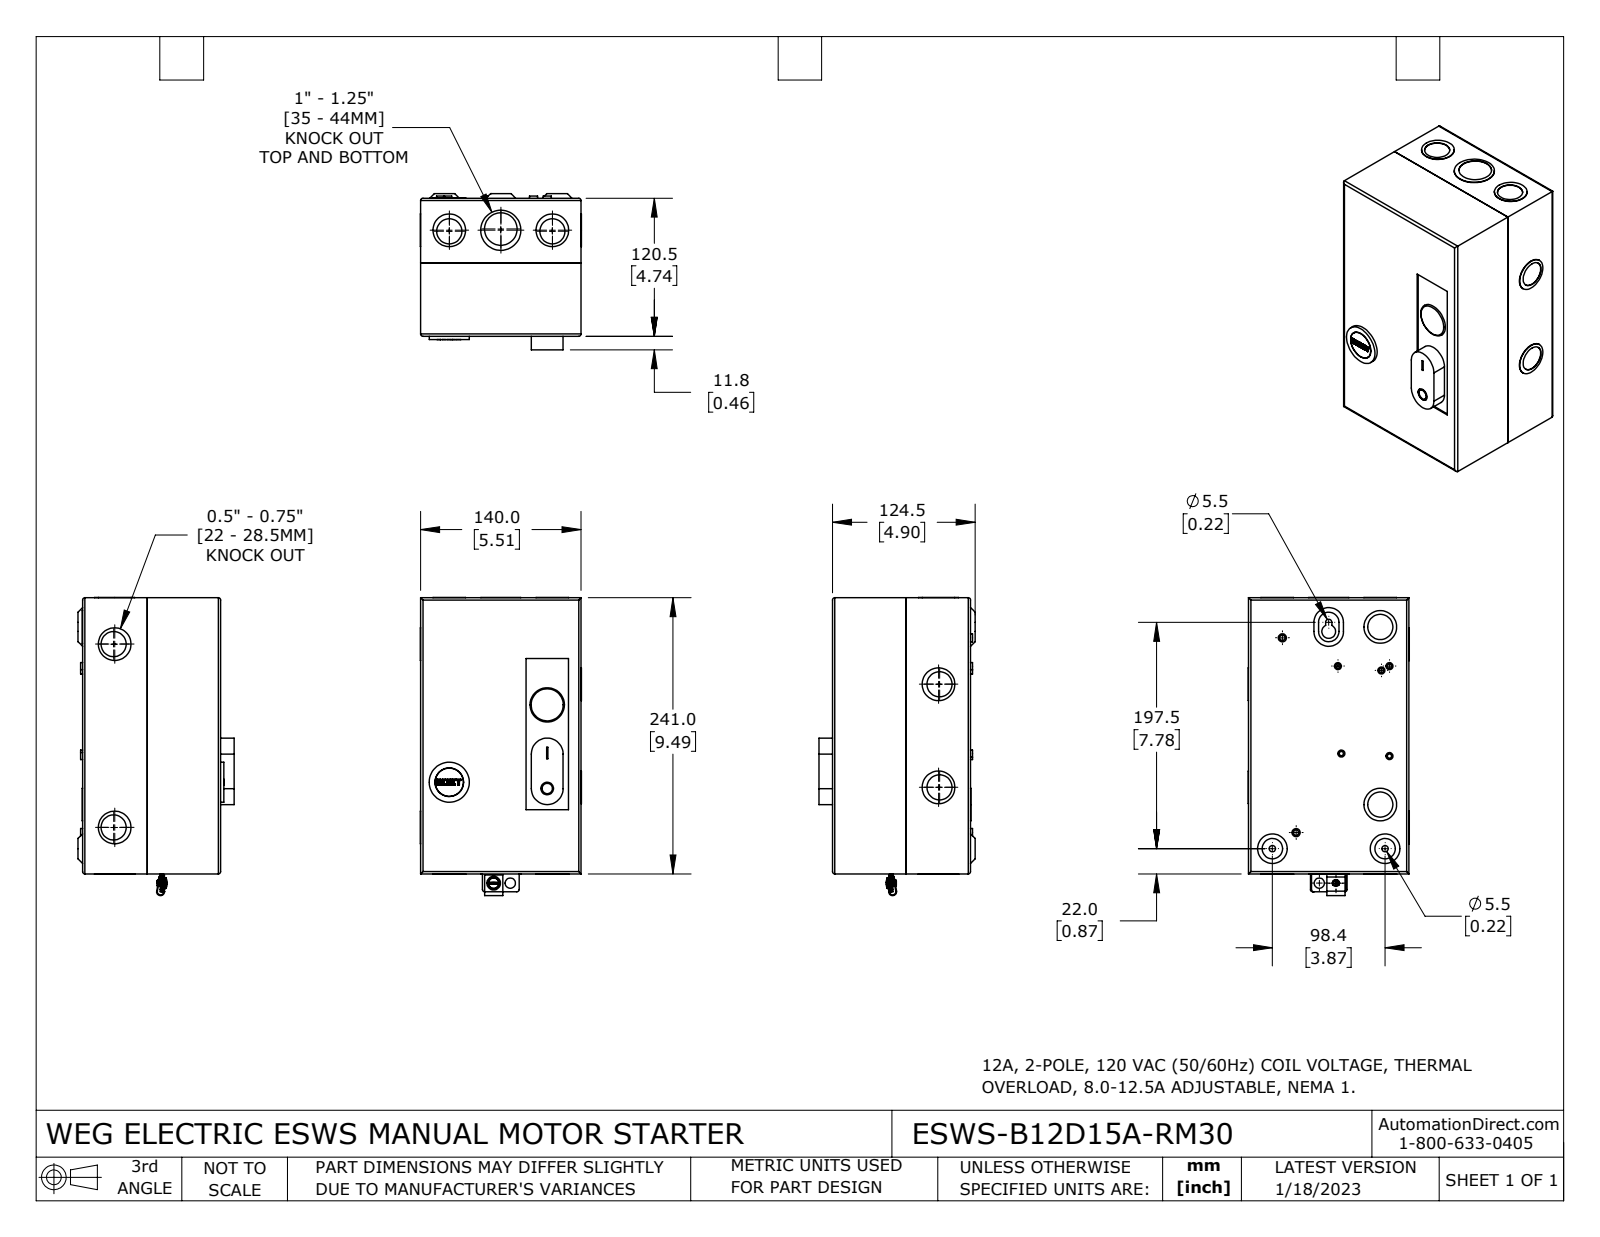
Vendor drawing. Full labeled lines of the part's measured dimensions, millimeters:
Part name (STEP PRODUCT): ESWS-B12D15A-RM30
STEP written by: SolidWorks 2021 (CONFIG_CONTROL_DESIGN)
Units: millimetres
Bodies: 7 solids, 435 faces (168 planar, 230 cylindrical, 37 other)
Overall size (bounding box): 260.3 × 140.6 × 136.3
Volume: 266 000 mm³ · Surface area: 377 500 mm²
Round holes (diameter × count): ⌀3.7 ×5, ⌀21.9 ×4, ⌀4.6 ×2, ⌀5.5 ×2, ⌀9 ×2, ⌀21.9 ×2, ⌀22 ×2, ⌀22.5 ×2, ⌀6.5 ×1, ⌀7.7 ×1, ⌀11 ×1, ⌀11.9 ×1
Round bosses / shafts (diameter × count): ⌀28.5 ×6, ⌀6.1 ×5, ⌀28.5 ×2, ⌀7.1 ×2, ⌀35.1 ×1, ⌀35 ×1, ⌀30.3 ×1, ⌀29.2 ×1
Partial cylindrical surfaces — rounded edges, fillets, slot ends (radius × count): R0.1 ×34, R2 ×13, R0.8 ×4, R2.7 ×3, R1.5 ×2, R1.9 ×2, R3.1 ×2, R3.5 ×2
Main face-to-face distances: 1.2, 119.3, 138.8, 118.1, 239.8, 120.5, 137.6, 140, 1.8, 1.6
Hole centre spacings: 14.5, 35, 45, 86, 90, 125, 152.3, 190.1
